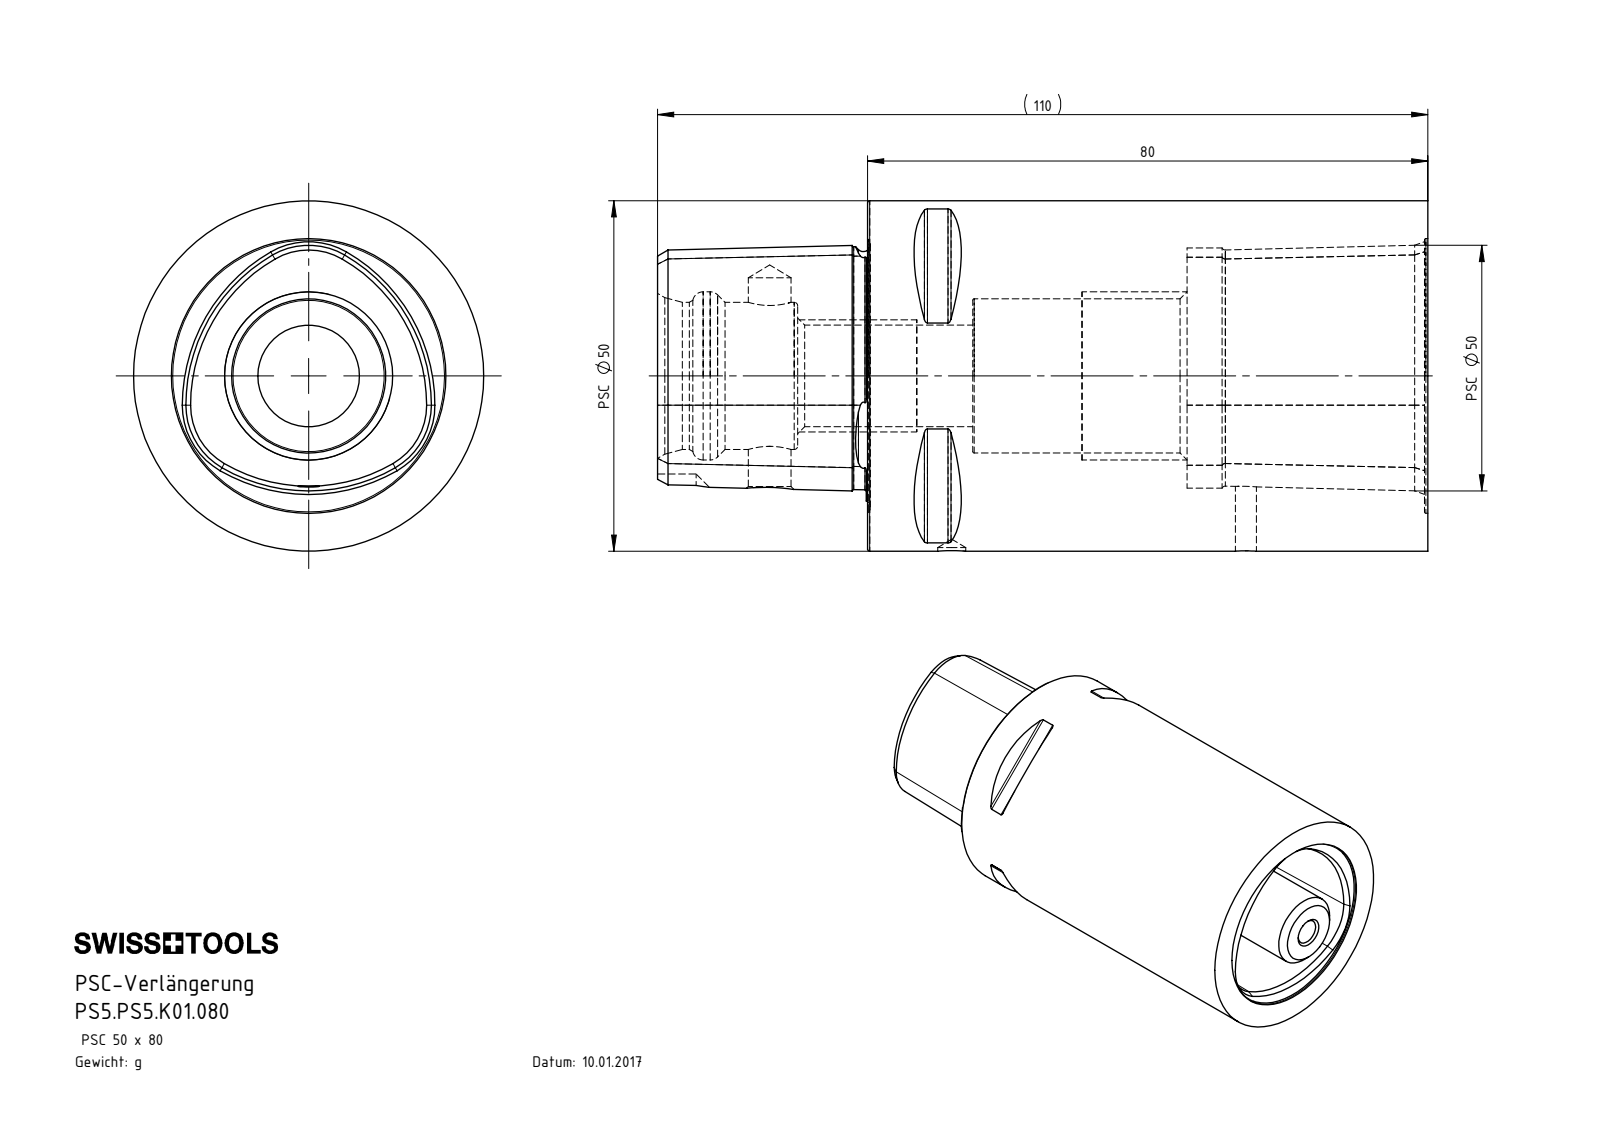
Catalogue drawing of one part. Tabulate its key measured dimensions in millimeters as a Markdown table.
| quantity | value |
| --- | --- |
| part name | PS5.PS5.K01.080; PS5-ER1.K01.070_A_PreviewCfg; PS5-PS5.K01.080_B; ISO 8745-3x10 (+1 more) |
| STEP written by | SolidWorks 2017 (AUTOMOTIVE_DESIGN) |
| units | millimeters |
| bodies | 4 solids, 333 faces (49 planar, 138 cylindrical, 146 other) |
| overall size | 114.5 × 50 × 50 |
| volume | 144 961 mm³ |
| surface area | 37 524 mm² |
| round holes (diameter × count) | 5.5 × 2, 3 × 1, 4 × 1, 6.1 × 1, 14.5 × 1, 16.4 × 1, 21 × 1, 22 × 1, 24 × 1, 39.2 × 1 |
| round bosses / shafts (diameter × count) | 50 × 1, 25.4 × 1, 21.6 × 1, 21.5 × 1, 16 × 1 |
| partial cylindrical surfaces (radius × count) | 0.5 × 8, 9.9 × 3, 24.38 × 3, 4 × 1 |
| main face-to-face distances | 80, 45.6, 34.4, 30, 75.6, 110, 45, 15, 30.6, 65 |
| hole center spacings | 26, 42, 68 |
